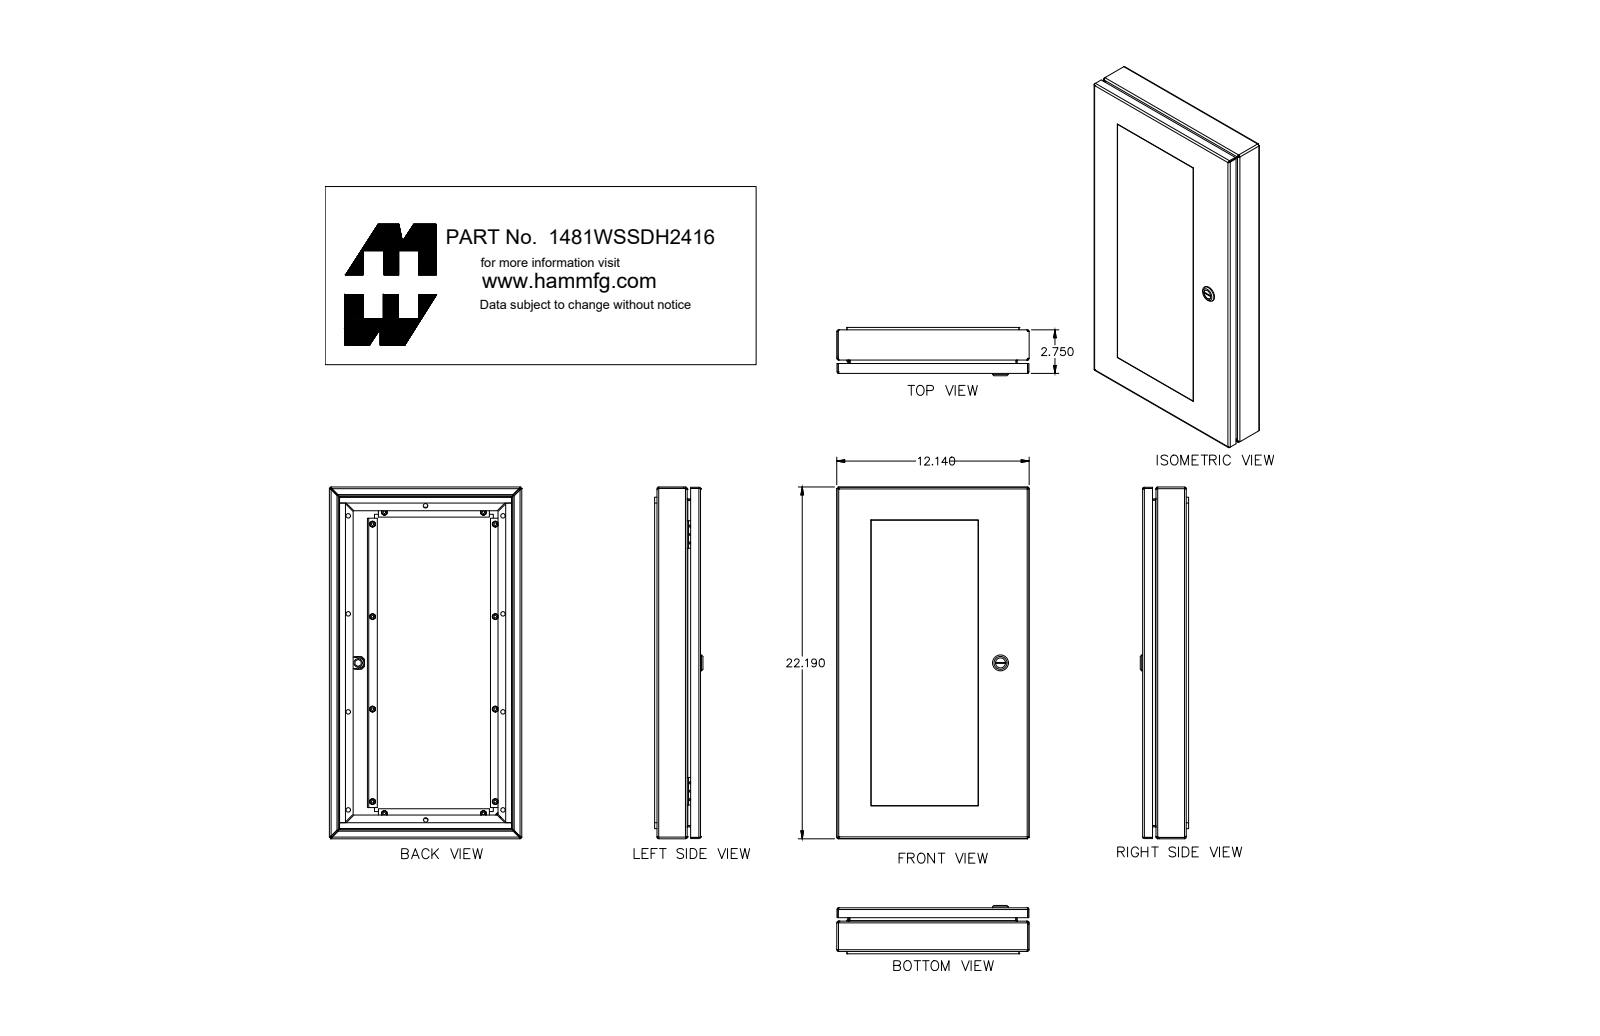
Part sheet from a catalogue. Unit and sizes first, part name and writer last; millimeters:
Units: millimetres
Overall size (bounding box): 563.6 × 308.4 × 73.9
Round holes (diameter × count): ⌀3.3 ×12, ⌀7.1 ×10, ⌀3.5 ×2, ⌀5 ×1, ⌀6.1 ×1, ⌀6.1 ×1, ⌀9.8 ×1, ⌀12.7 ×1, ⌀16 ×1, ⌀19.5 ×1
Round bosses / shafts (diameter × count): ⌀9.3 ×12, ⌀5.7 ×12, ⌀4.2 ×12, ⌀27.9 ×1, ⌀19.9 ×1, ⌀15.9 ×1, ⌀13.3 ×1, ⌀12.1 ×1
Partial cylindrical surfaces — rounded edges, fillets, slot ends (radius × count): R0.9 ×28, R2.7 ×28, R2.6 ×24, R0.4 ×4, R2.2 ×4, R3.2 ×2, R0.5 ×1, R0.7 ×1
Main face-to-face distances: 1.8, 6.4, 4.5, 65.5, 21.4, 44.1, 59.1, 306.5, 15, 67.3
Hole centre spacings: 246.4, 293.5, 125, 148.2, 157, 178.8, 196.9, 248
Volume: 1 174 000 mm³ · Surface area: 913 500 mm²
Bodies: 46 solids, 1077 faces (579 planar, 308 cylindrical, 190 other)
Part name (STEP PRODUCT): 1481WSSDH2416_Default
STEP written by: SolidWorks 2019 (CONFIG_CONTROL_DESIGN)
